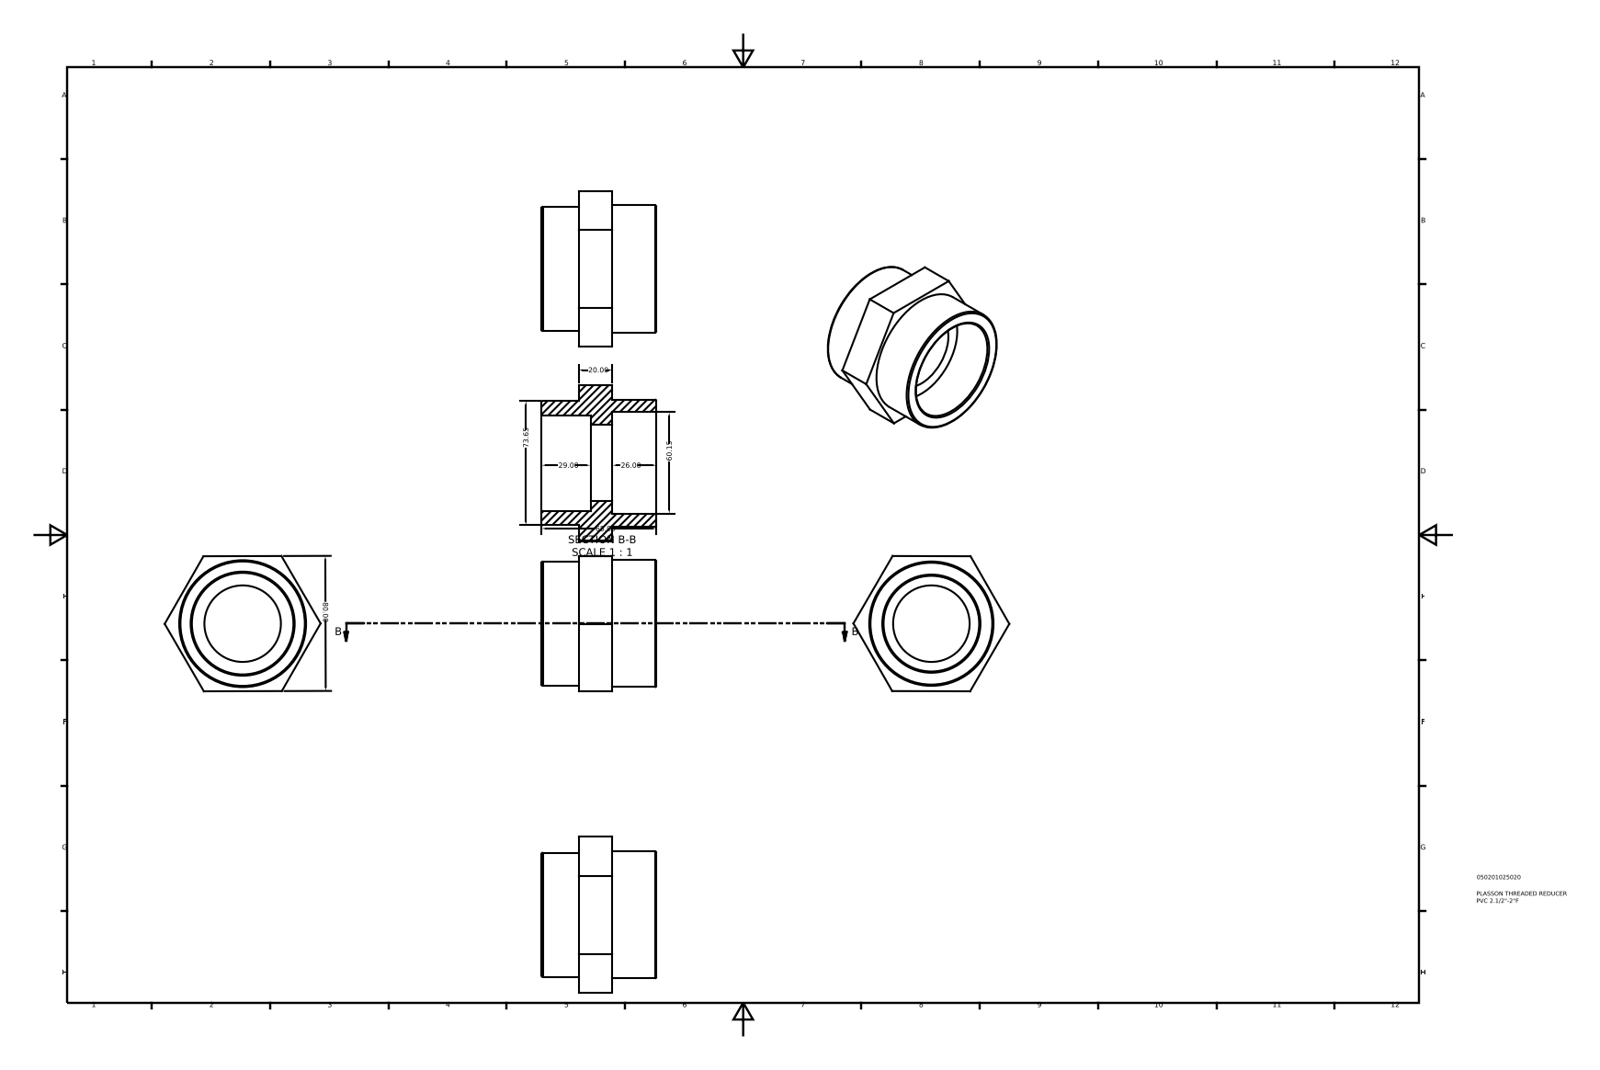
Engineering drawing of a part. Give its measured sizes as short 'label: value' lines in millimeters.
name: 050201025020
written by: Autodesk Inventor 2015 (AUTOMOTIVE_DESIGN)
unit: mm
bodies: 1 solid, 21 faces (12 planar, 5 cylindrical, 4 other)
size: 92.38 × 80.14 × 68
volume: 151 951 mm³; area: 36 289 mm²
holes: 1× ⌀45.32, 1× ⌀56.66, 1× ⌀60.15
bosses: 1× ⌀75.18, 1× ⌀73.65
face distances: 42, 22, 20, 68, 46, 26, 80, 80.04, 80.06, 29
